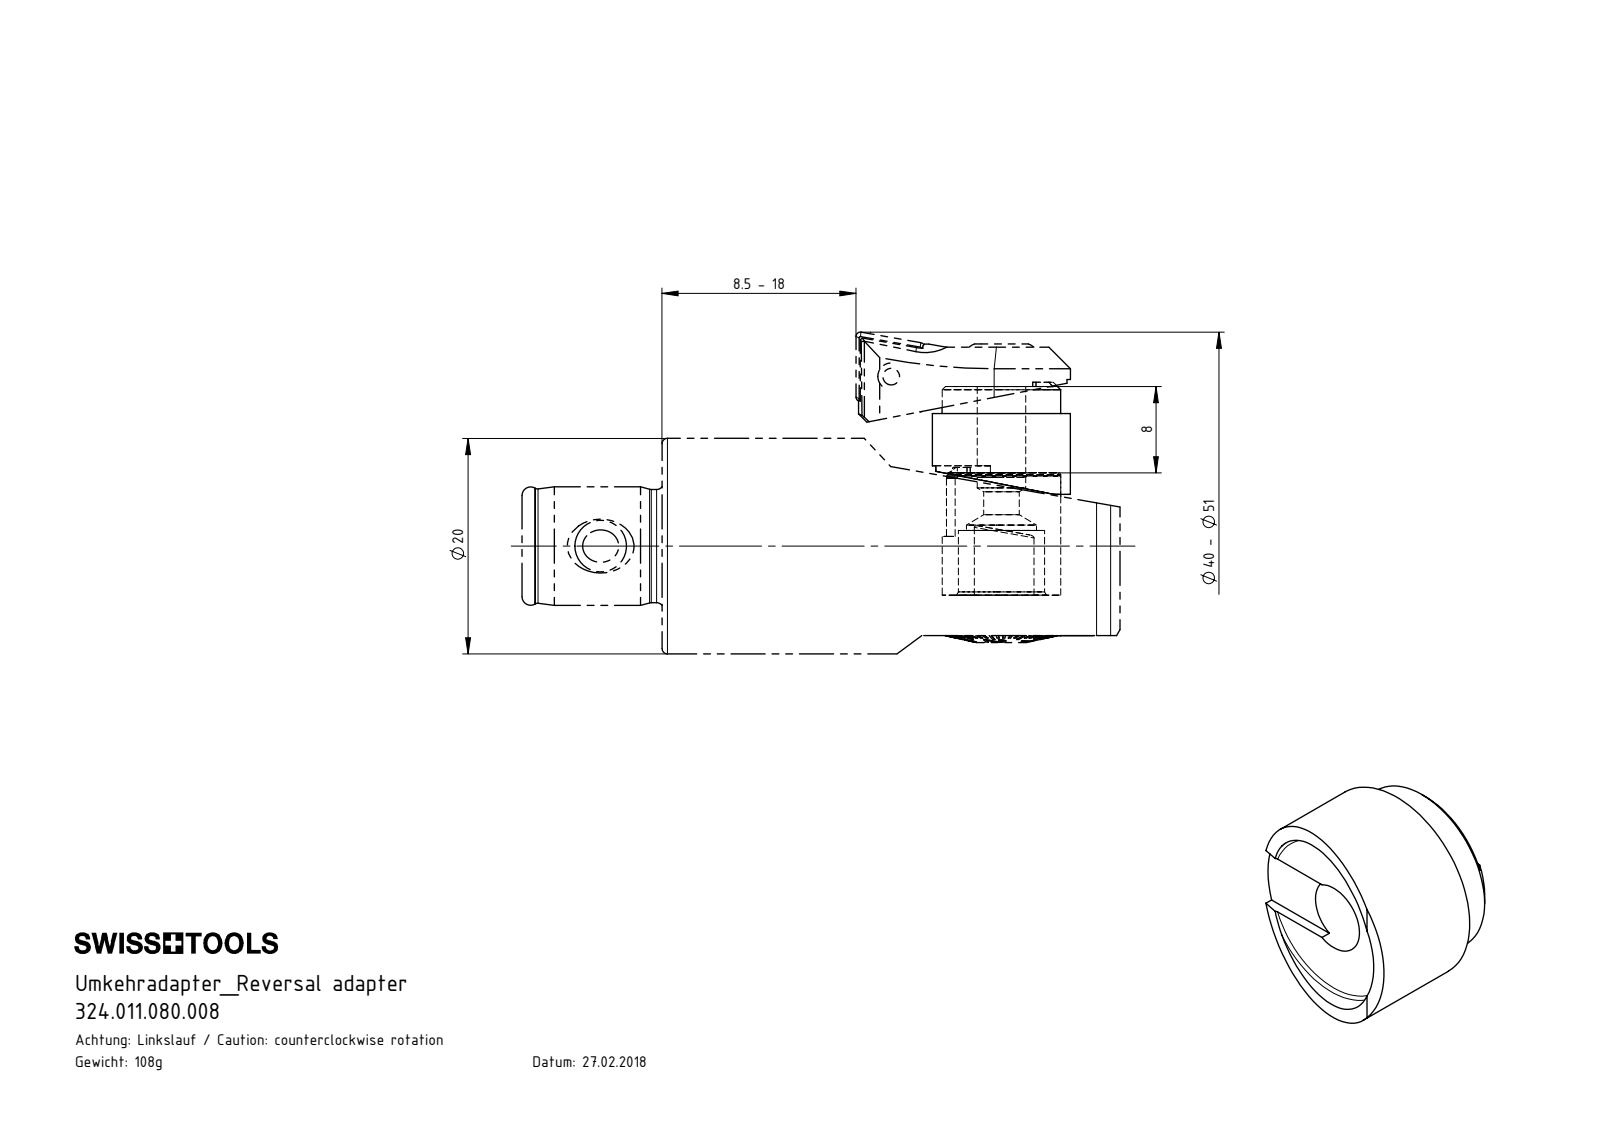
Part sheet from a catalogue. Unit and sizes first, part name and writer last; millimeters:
Units: millimetres
Overall size (bounding box): 12.8 × 12.8 × 10.4
Round holes (diameter × count): ⌀4.5 ×1, ⌀11 ×1
Round bosses / shafts (diameter × count): ⌀12.8 ×1
Partial cylindrical surfaces — rounded edges, fillets, slot ends (radius × count): R0.3 ×2
Main face-to-face distances: 8, 2.5, 5.5, 7.35, 4.85, 0.65, 0.4, 2.9, 7.75, 8.4
Volume: 843 mm³ · Surface area: 719 mm²
Bodies: 1 solid, 29 faces (13 planar, 11 cylindrical, 5 other)
Part name (STEP PRODUCT): 324.011.080.008; F20-U00.001.008_B
STEP written by: SolidWorks 2017 (CONFIG_CONTROL_DESIGN)
